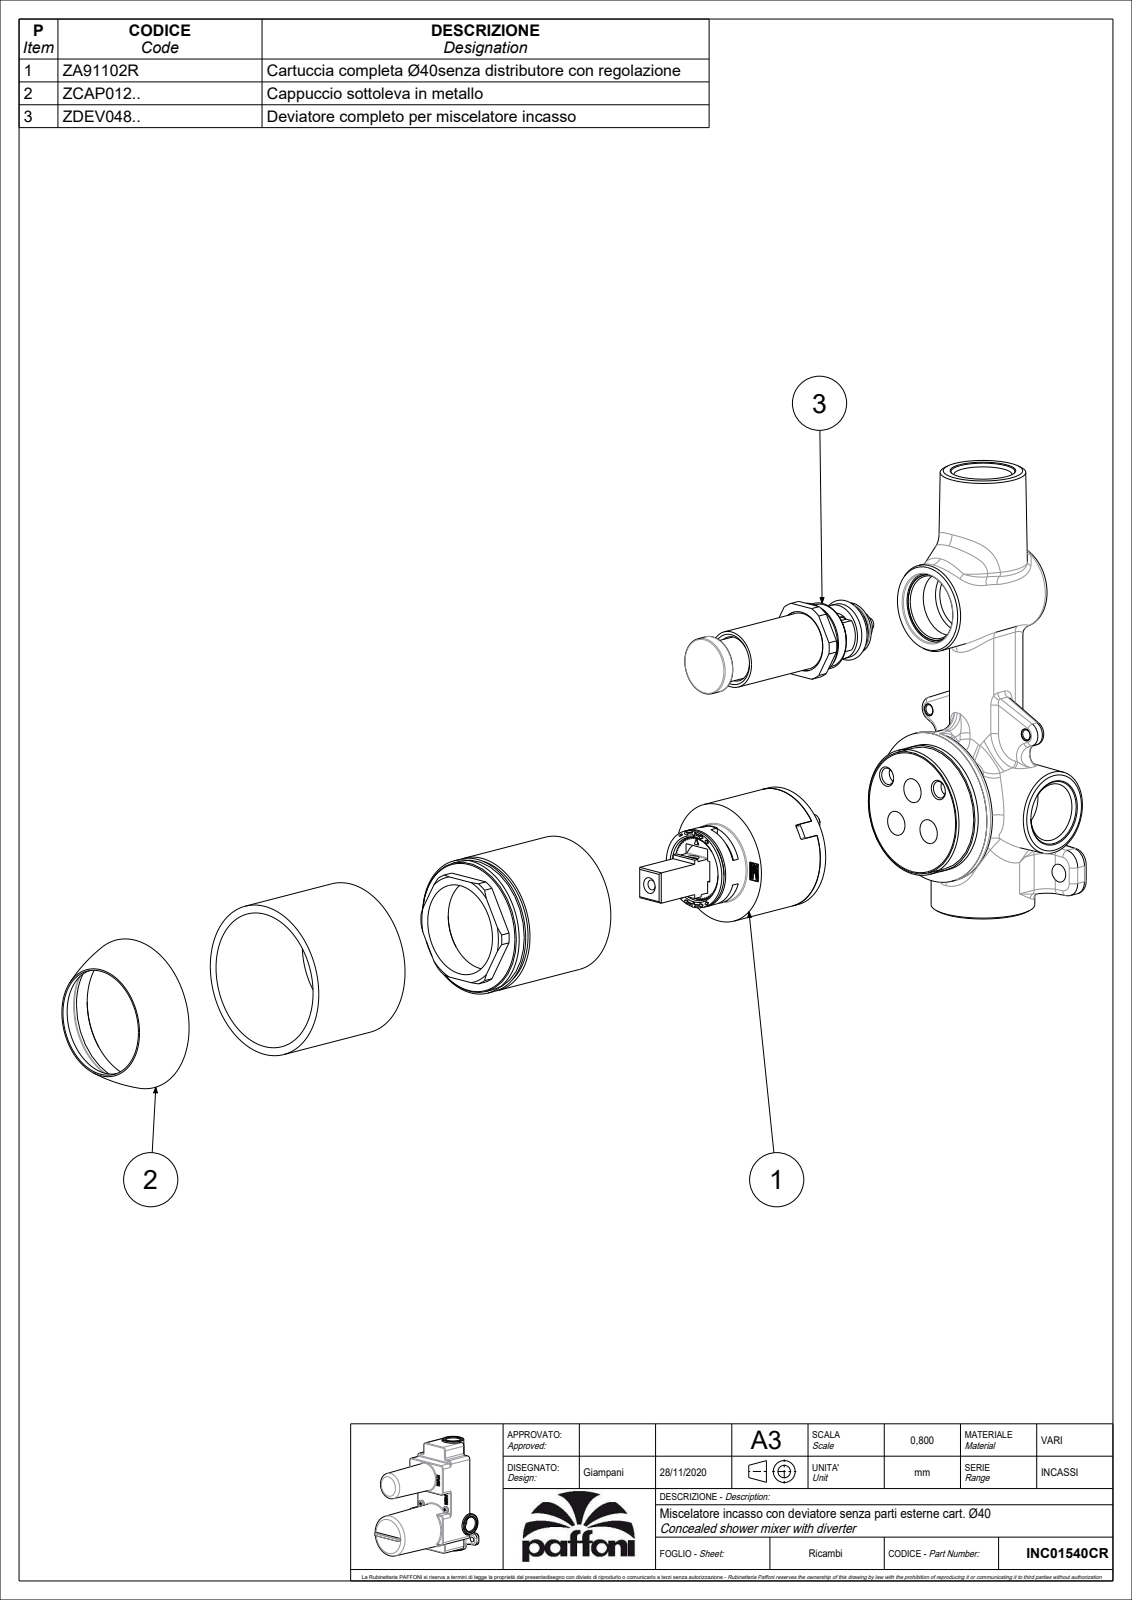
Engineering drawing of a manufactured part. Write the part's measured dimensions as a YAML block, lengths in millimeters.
part_name: "INC01540CR"
step_written_by: "CREO PARAMETRIC BY PTC INC, 2020044 (CONFIG_CONTROL_DESIGN)"
units: millimeters
bodies: {solids: 1, faces: 1952, planar: 750, cylindrical: 538, other: 664}
overall_size: [148, 143.3, 66]
volume: 277011
surface_area: 169684
round_holes:
  - {diameter: 8, count: 7}
  - {diameter: 6, count: 3}
  - {diameter: 19, count: 3}
  - {diameter: 3.3, count: 2}
  - {diameter: 4.2, count: 2}
  - {diameter: 11, count: 2}
  - {diameter: 11.7, count: 2}
  - {diameter: 21, count: 2}
  - {diameter: 3, count: 1}
  - {diameter: 4, count: 1}
  - {diameter: 4.1, count: 1}
  - {diameter: 4.3, count: 1}
round_bosses_or_shafts:
  - {diameter: 4, count: 3}
  - {diameter: 8, count: 2}
  - {diameter: 7.8, count: 2}
  - {diameter: 50.3, count: 1}
  - {diameter: 50, count: 1}
  - {diameter: 39.5, count: 1}
  - {diameter: 36.7, count: 1}
  - {diameter: 34, count: 1}
partial_cylinders:
  - {radius: 2, count: 53}
  - {radius: 1, count: 43}
  - {radius: 0.2, count: 36}
  - {radius: 0.5, count: 30}
  - {radius: 4, count: 22}
  - {radius: 1.5, count: 8}
  - {radius: 5, count: 7}
  - {radius: 3, count: 4}
face_to_face_distances: [2, 60, 11, 13, 85, 49, 58, 15, 38, 62]
hole_center_spacings: [0.54, 8.7, 8.83, 9.7, 9.9, 14.21, 14.43, 14.76]
